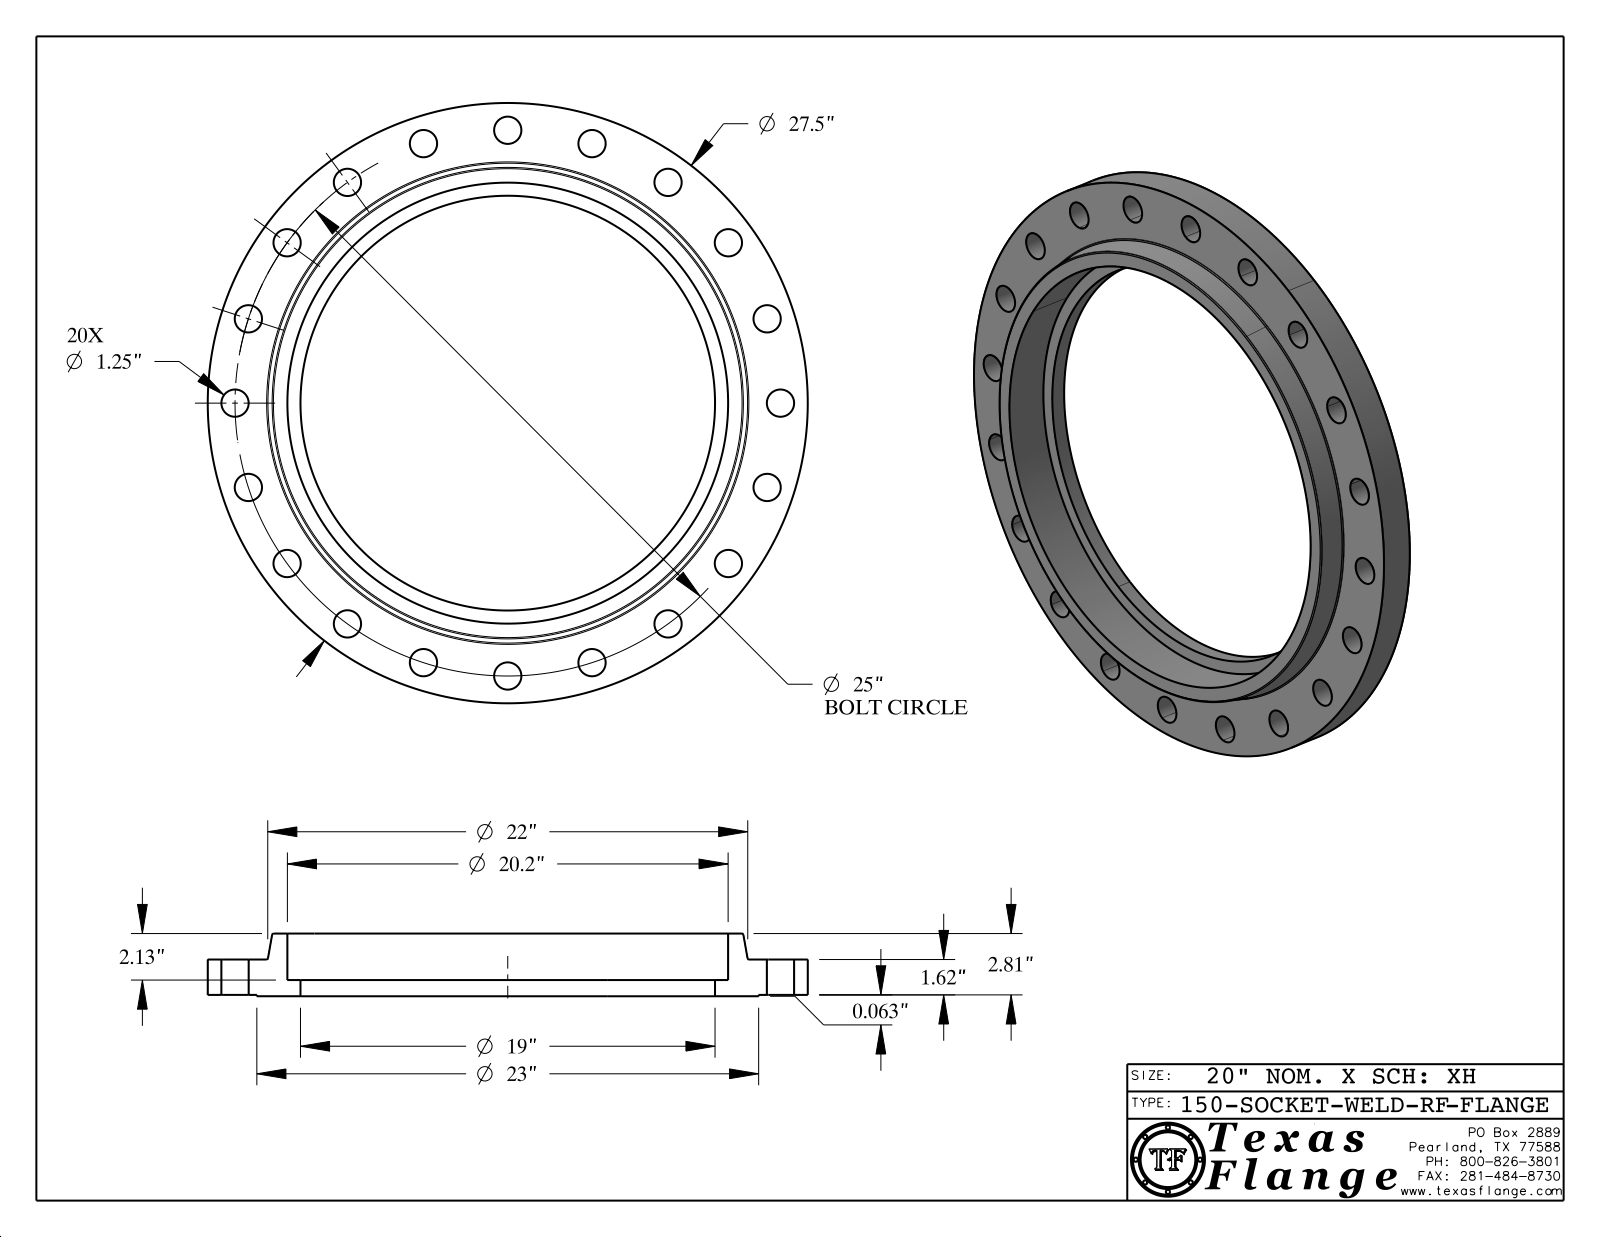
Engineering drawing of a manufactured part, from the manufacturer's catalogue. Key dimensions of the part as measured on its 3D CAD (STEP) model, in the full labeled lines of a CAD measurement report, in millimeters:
Part name (STEP PRODUCT): 150-SOCKET-WELD-RF
STEP written by: CATIA V5 STEP AP214 (AUTOMOTIVE_DESIGN)
Units: millimetres
Bodies: 1 solid, 444 faces (370 planar, 68 cylindrical, 6 other)
Overall size (bounding box): 698.5 × 698.5 × 73
Volume: 8 179 000 mm³ · Surface area: 702 600 mm²
Round holes (diameter × count): ⌀31.8 ×20, ⌀12.6 ×1, ⌀482.6 ×1, ⌀513.1 ×1
Round bosses / shafts (diameter × count): ⌀0.8 ×8, ⌀698.5 ×1, ⌀584.2 ×1, ⌀9.9 ×1
Main face-to-face distances: 41.1, 1.6, 42.7, 72.9, 71.4, 30.2, 18.9, 17.3, 23.9, 54.1
Hole centre spacings: 317.5, 373.2, 449, 513.7, 603.9, 627.2, 288.3, 565.8
